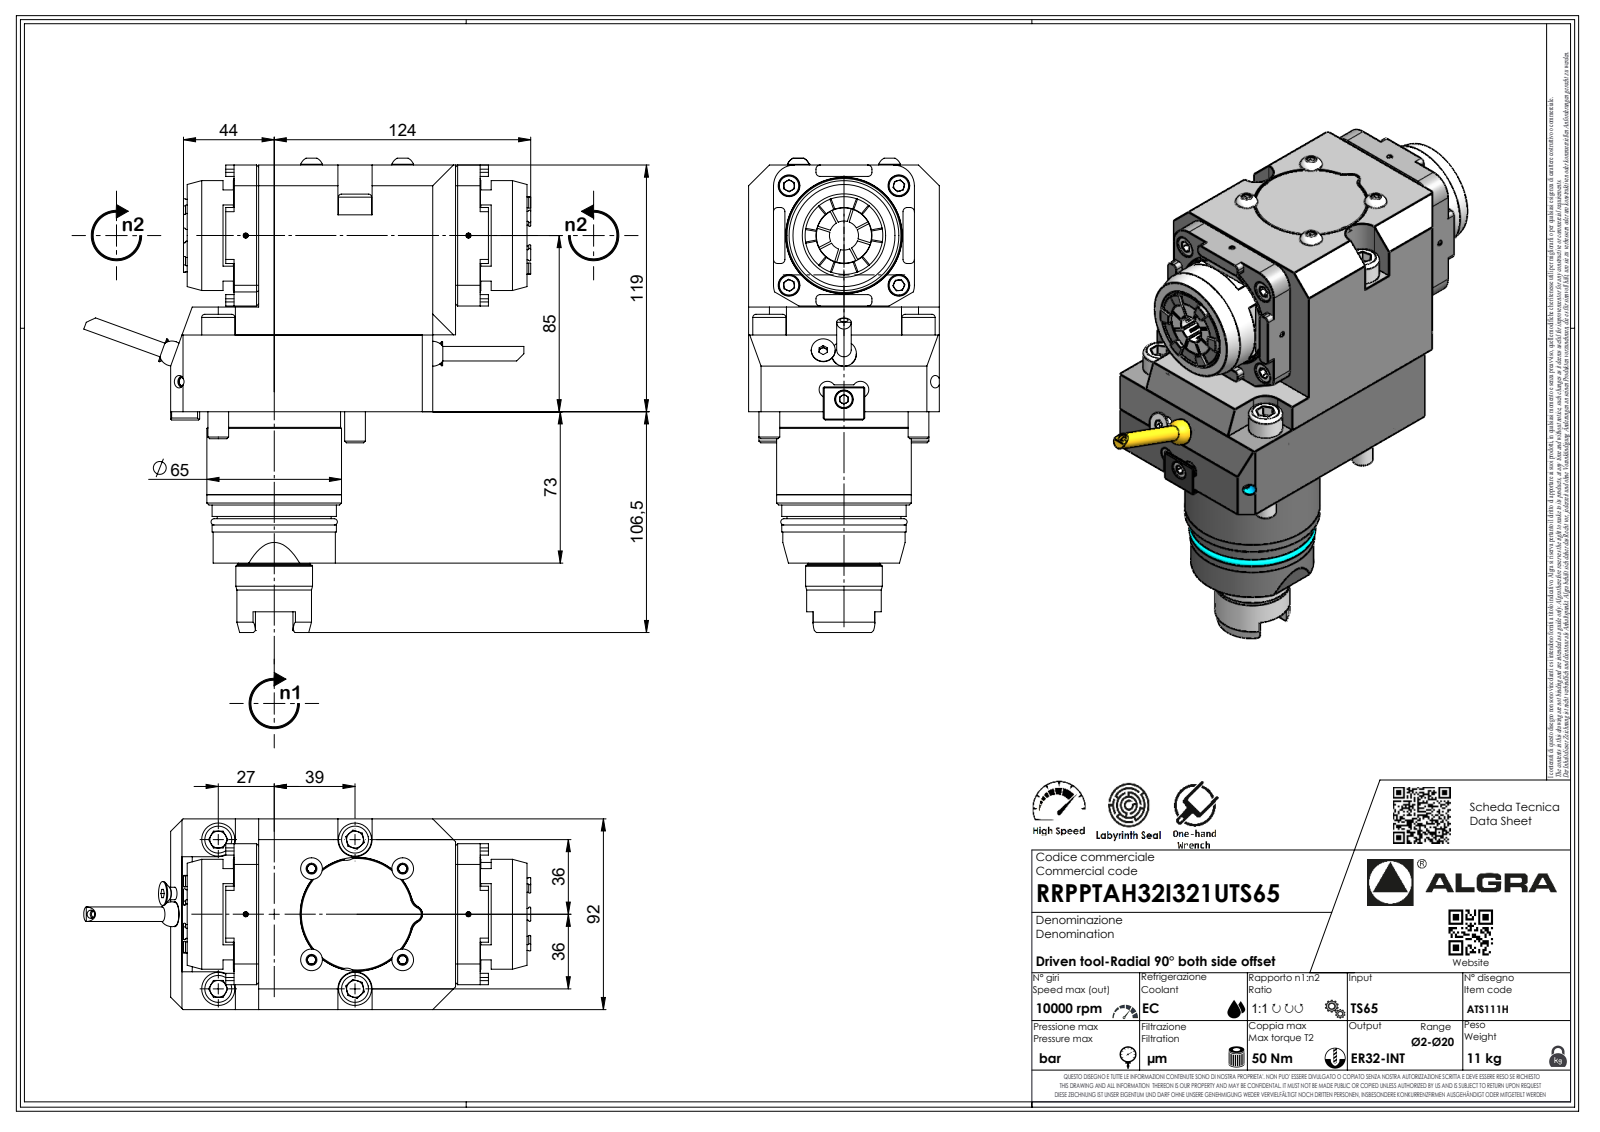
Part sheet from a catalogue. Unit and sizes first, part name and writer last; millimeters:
Units: millimetres
Overall size (bounding box): 228.8 × 213.91 × 92
Round holes (diameter × count): ⌀4 ×2, ⌀2.1 ×1
Round bosses / shafts (diameter × count): ⌀10.5 ×4, ⌀10 ×4, ⌀16 ×2, ⌀7 ×2, ⌀65 ×1, ⌀64.98 ×1, ⌀64 ×1, ⌀60 ×1
Partial cylindrical surfaces — rounded edges, fillets, slot ends (radius × count): R2 ×16, R0.33 ×7, R0.52 ×7, R3.7 ×7, R0.75 ×4, R10 ×4, R8.25 ×2, R0.21 ×1
Main face-to-face distances: 92, 119, 12, 50.5, 68, 22.6, 141.4, 129.5, 34.5, 11.9
Volume: 1 627 000 mm³ · Surface area: 111 676 mm²
Bodies: 3 solids, 615 faces (379 planar, 102 cylindrical, 134 other)
Part name (STEP PRODUCT): RRPPTAH32I321UTS65
STEP written by: SolidWorks 2023 (AUTOMOTIVE_DESIGN)
